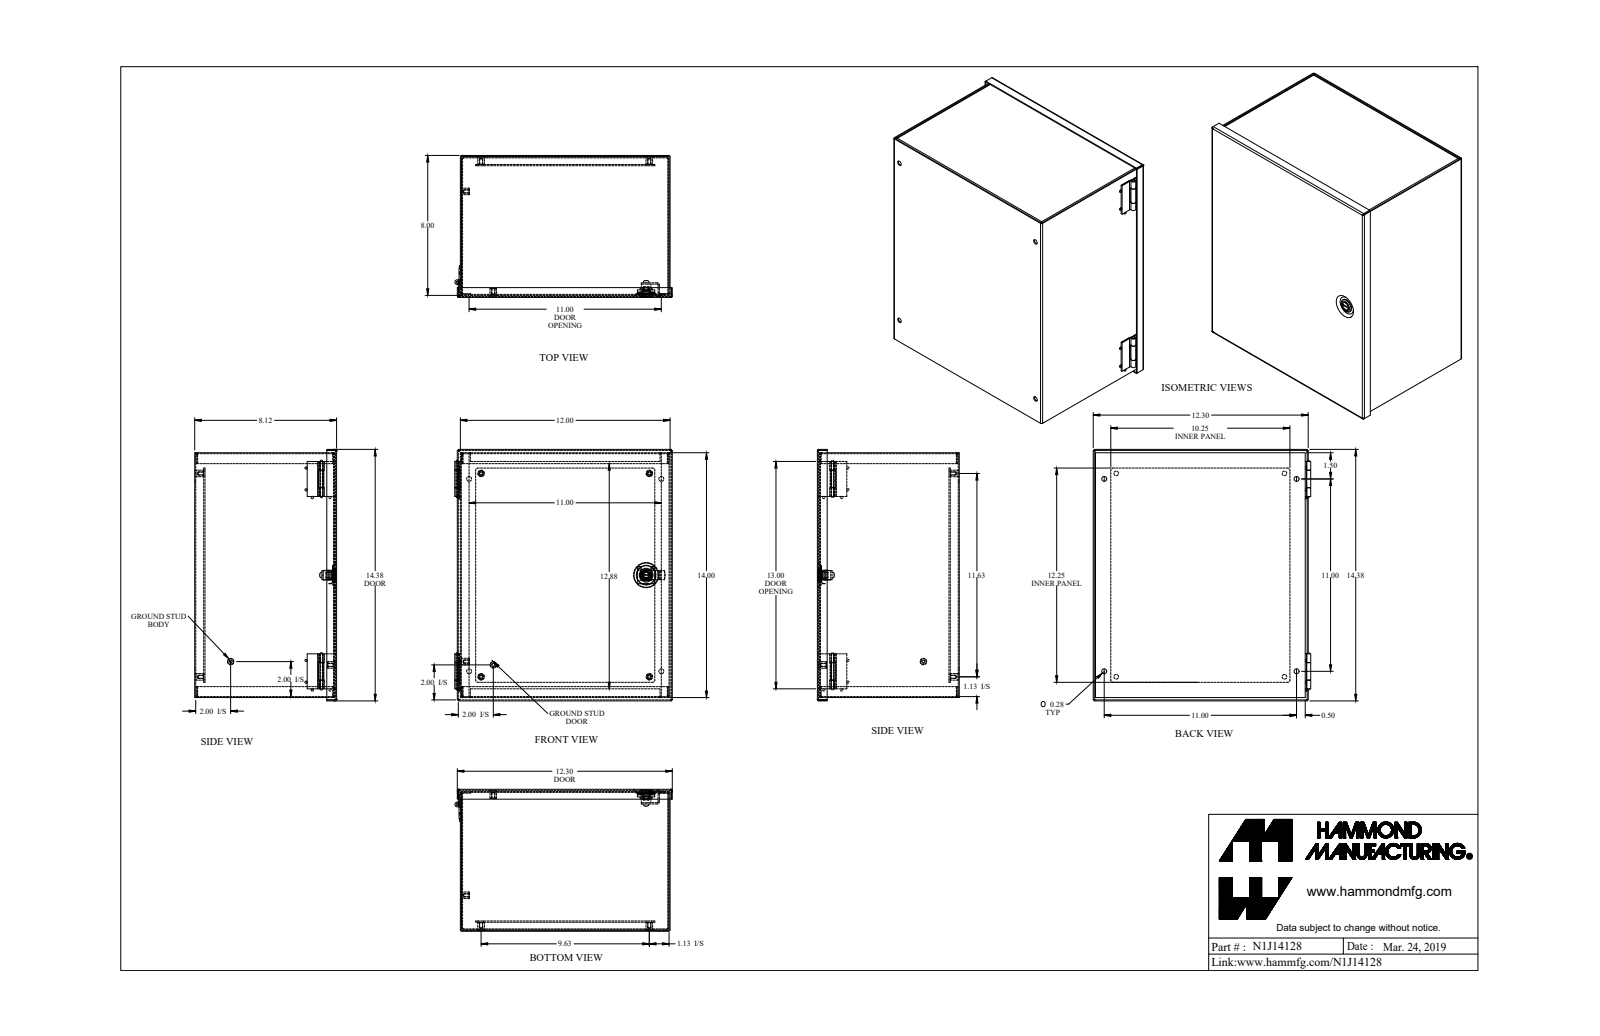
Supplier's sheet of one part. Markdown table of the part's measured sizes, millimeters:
| quantity | value |
| --- | --- |
| part name | N1J14128 |
| STEP written by | SolidWorks 2018 (AUTOMOTIVE_DESIGN) |
| units | millimeters |
| bodies | 18 solids, 477 faces (224 planar, 188 cylindrical, 65 other) |
| overall size | 365.3 × 316.1 × 206.2 |
| volume | 942 700 mm³ |
| surface area | 1 264 000 mm² |
| round holes (diameter × count) | 4 × 6, 6.7 × 4, 7.1 × 4, 3.2 × 1, 8.1 × 1, 12.1 × 1 |
| round bosses / shafts (diameter × count) | 3.3 × 8, 9.5 × 6, 20 × 1, 13.9 × 1, 12 × 1, 11.9 × 1, 9.3 × 1, 8.1 × 1 |
| partial cylindrical surfaces (radius × count) | 0.7 × 16, 2.2 × 16, 0.3 × 4, 2.5 × 4, 3.2 × 4, 0.9 × 2, 2 × 2, 6.4 × 2 |
| main face-to-face distances | 1.4, 204.7, 303.4, 354.2, 203.3, 206.2, 1.8, 13.1, 11.7, 191.6 |
| hole center spacings | 19.2, 262.1, 279.4, 287.9, 388.8, 141.5, 147.7, 244.5 |
